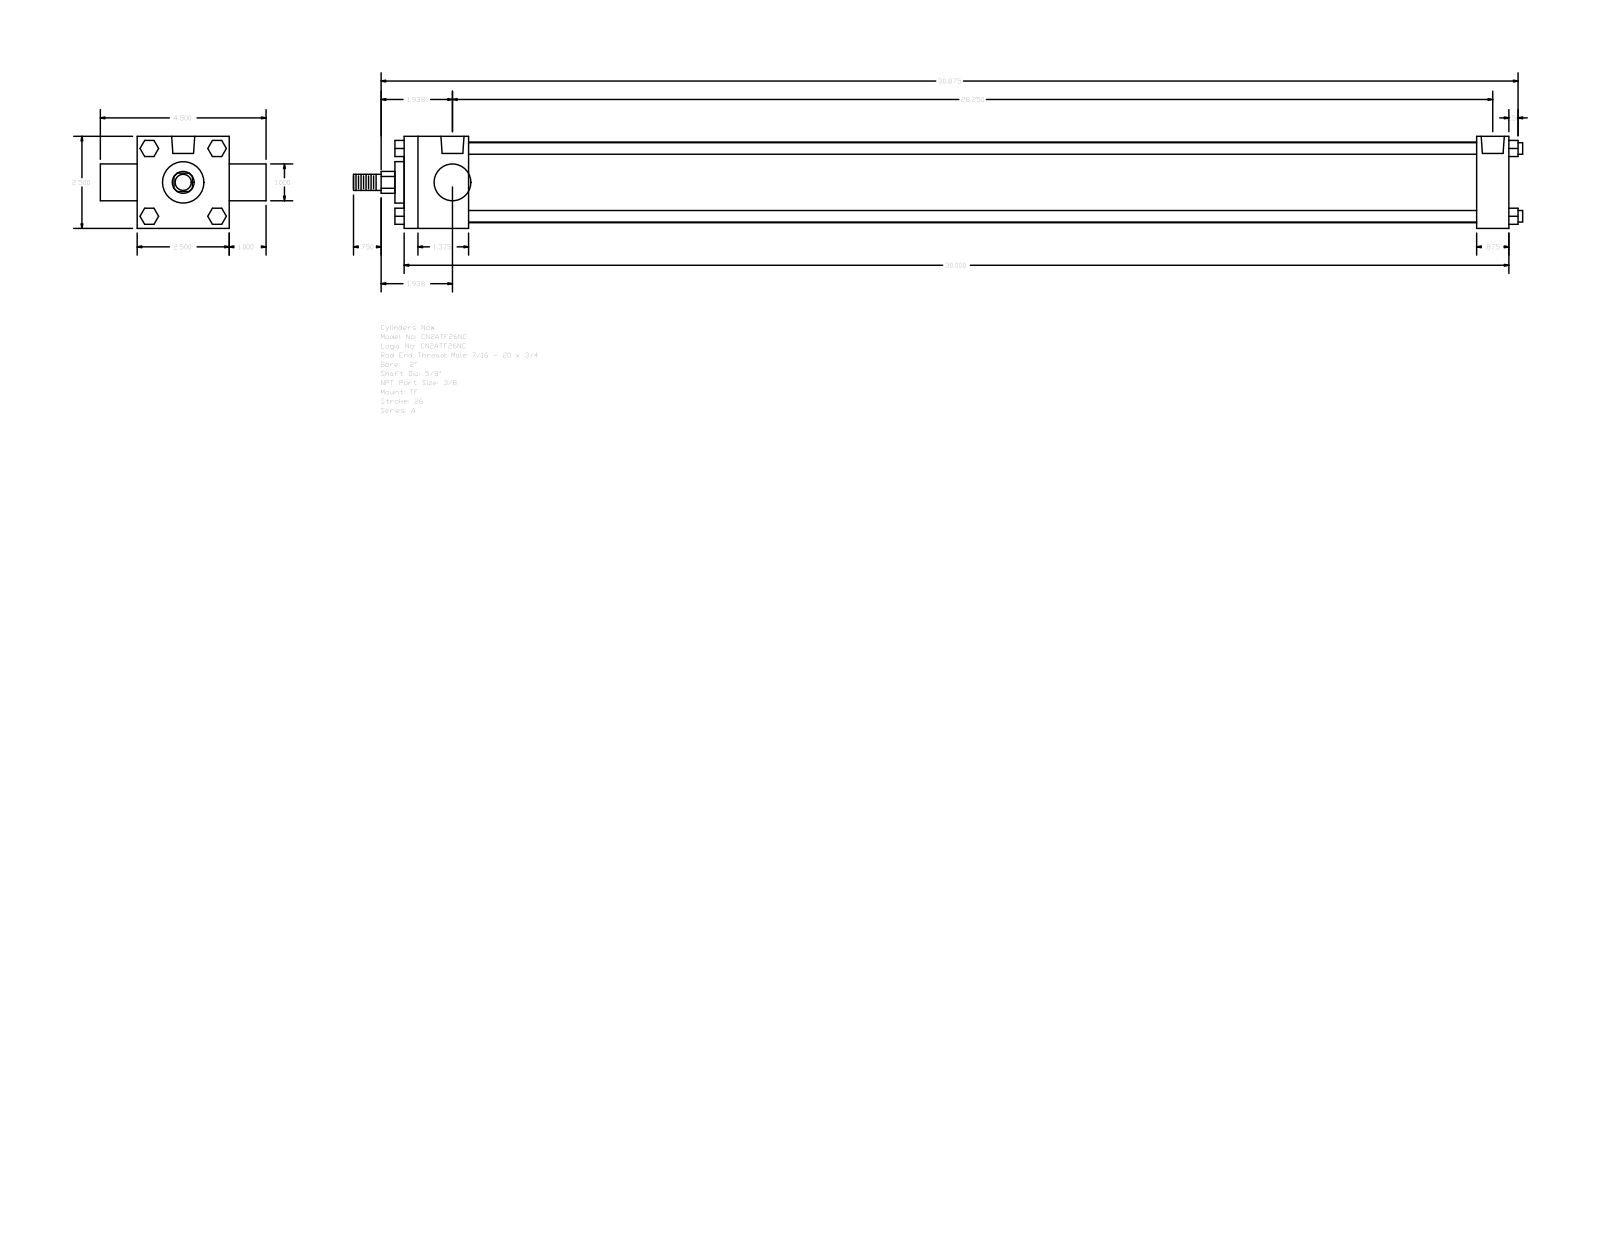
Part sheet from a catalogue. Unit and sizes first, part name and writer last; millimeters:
Units: millimetres
Overall size (bounding box): 806.45 × 114.3 × 63.5
Round holes (diameter × count): ⌀5.56 ×3, ⌀15.93 ×2
Round bosses / shafts (diameter × count): ⌀7.94 ×4, ⌀55.63 ×1, ⌀28.57 ×1, ⌀25.4 ×1, ⌀15.88 ×1, ⌀11.11 ×1
Partial cylindrical surfaces — rounded edges, fillets, slot ends (radius × count): R7.54 ×1
Main face-to-face distances: 63.5, 762, 44.45, 739.77, 695.32, 717.55, 22.23, 25.4, 88.9, 6.35
Hole centre spacings: 3.97, 3.98, 709.6, 713.57, 713.58, 717.55
Bodies: 0 solids, 120 faces (92 planar, 28 cylindrical, 0 other)
Part name (STEP PRODUCT): A_TF__0200_0.625
STEP written by: GSSL Pune (CONFIG_CONTROL_DESIGN)
